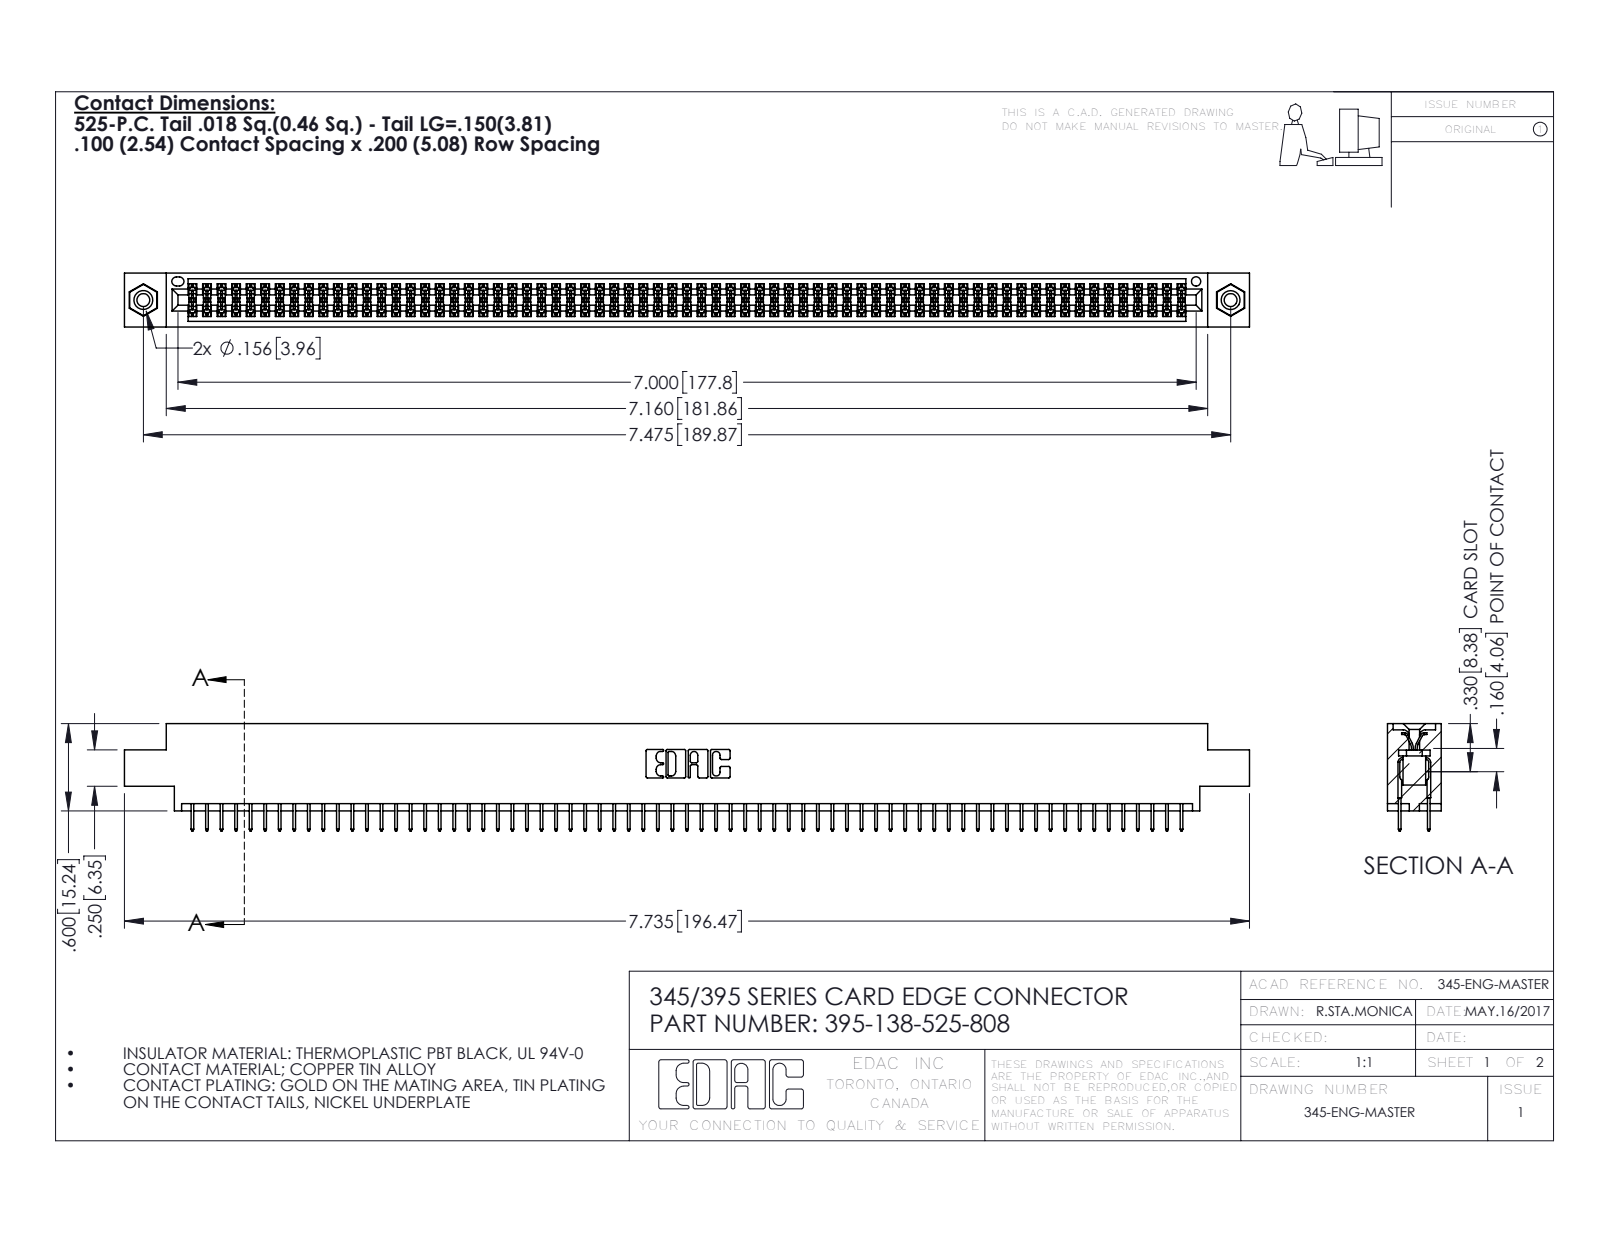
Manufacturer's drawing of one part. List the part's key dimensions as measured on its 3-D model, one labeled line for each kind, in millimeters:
Part name (STEP PRODUCT): 345-292-001_345-293-125; 395-138-525-808; 345-250-001_345-250-003-102; 345 Part_0.170 Offset - 0.156 Dia-TI
STEP written by: SolidWorks 2020 (CONFIG_CONTROL_DESIGN)
Units: millimetres
Bodies: 141 solids, 7642 faces (5498 planar, 2128 cylindrical, 16 other)
Overall size (bounding box): 196.5 × 18.7 × 9.4
Volume: 18 990 mm³ · Surface area: 28 060 mm²
Round holes (diameter × count): ⌀2.3 ×2, ⌀3.2 ×2, ⌀4 ×2, ⌀1.6 ×1
Round bosses / shafts (diameter × count): ⌀3.9 ×2
Partial cylindrical surfaces — rounded edges, fillets, slot ends (radius × count): R0.2 ×207, R0.3 ×22, R0.2 ×6, R0.8 ×6, R0.7 ×3, R0.4 ×2, R0.5 ×2, R0.6 ×2
Main face-to-face distances: 1.8, 7.6, 9.4, 5.1, 2.5, 6.9, 0.6, 5.7, 1.8, 4.4
Hole centre spacings: 6.9, 183.9, 189.9
